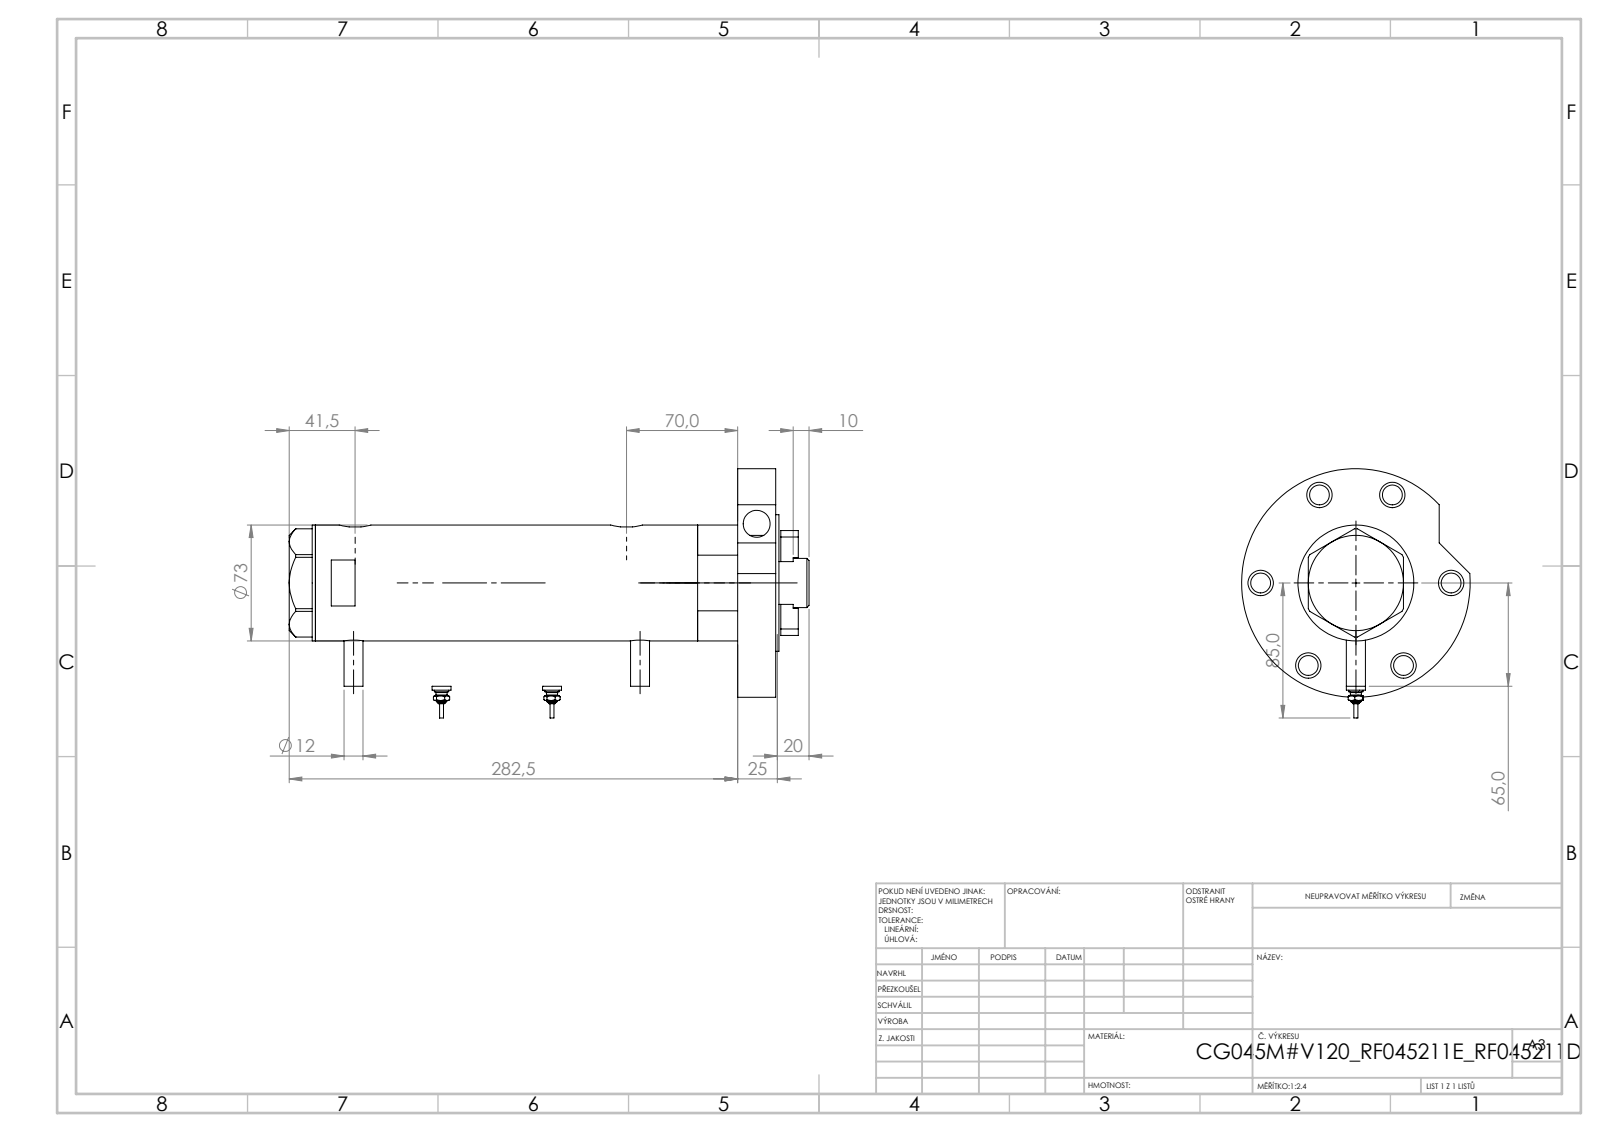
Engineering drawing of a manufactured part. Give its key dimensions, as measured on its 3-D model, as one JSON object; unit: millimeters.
{"part_name": "V270CG_RF211D; V270CG_MIDDLE; V270CG_RF211E; V270CG_SWITCH (+3 more)", "step_written_by": "SolidWorks 2019 (CONFIG_CONTROL_DESIGN)", "units": "millimeters", "bodies": {"solids": 9, "faces": 315, "planar": 113, "cylindrical": 128, "other": 74}, "overall_size": [311.52, 144, 144], "volume_mm3": 1359000, "surface_area_mm2": 236794, "round_holes": [[12.5, 8], [16, 6], [8.1, 4], [13.5, 4], [5, 2], [13.16, 2], [10.5, 1], [17, 1], [32, 1], [33.5, 1], [45, 1], [48, 1]], "round_bosses_or_shafts": [[12, 3], [9, 2], [7, 2], [4.34, 2], [2.4, 2], [144, 1], [86, 1], [73, 1]], "partial_cylinders_radius": [[10, 2]], "face_to_face_distances": [24, 247.45, 26, 271.45, 2, 273.45, 187.14, 60.31, 84.31, 161.14], "hole_center_spacings": [60, 25.14, 57.72, 71.64, 15, 35.04, 35.9, 43.78]}
